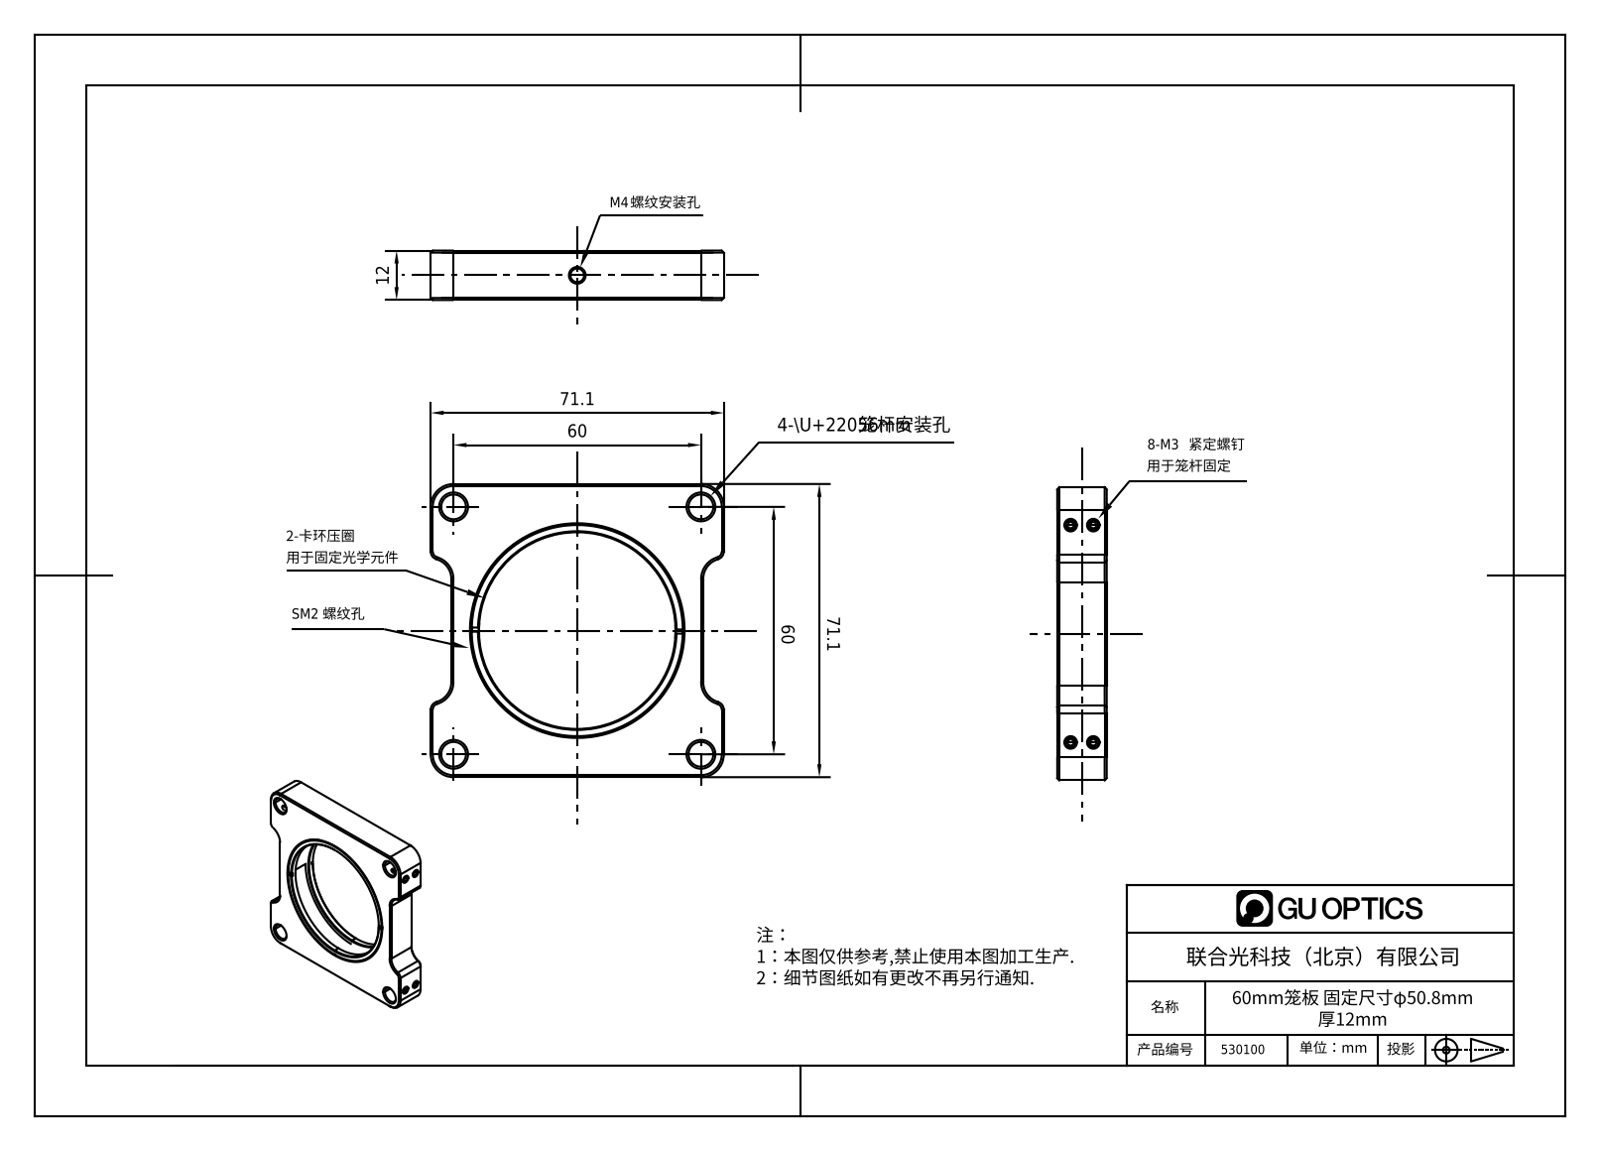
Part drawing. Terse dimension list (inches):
name: 2.3.1.2_L60B-SM2_60mm笼板，用于2.0英寸光学元件，12mm厚，附带两个SM2卡环，M4螺纹
written by: SolidWorks 2018 (AUTOMOTIVE_DESIGN)
unit: in
bodies: 0 solids, 294 faces (100 planar, 44 cylindrical, 150 other)
size: 2.799 × 2.799 × 0.472
holes: 4× ⌀0.098, 4× ⌀0.236, 1× ⌀0.13, 1× ⌀1.878, 1× ⌀2.01
rounds: 4× R0.079, 4× R0.197, 4× R0.219
face distances: 0.472, 2.799, 0.098, 0.374, 0.197, 2.602, 2.406, 0.276, 2.285, 0.139
hole spacings: 1.67, 2.362, 0.217, 2.075, 2.086, 3.341
